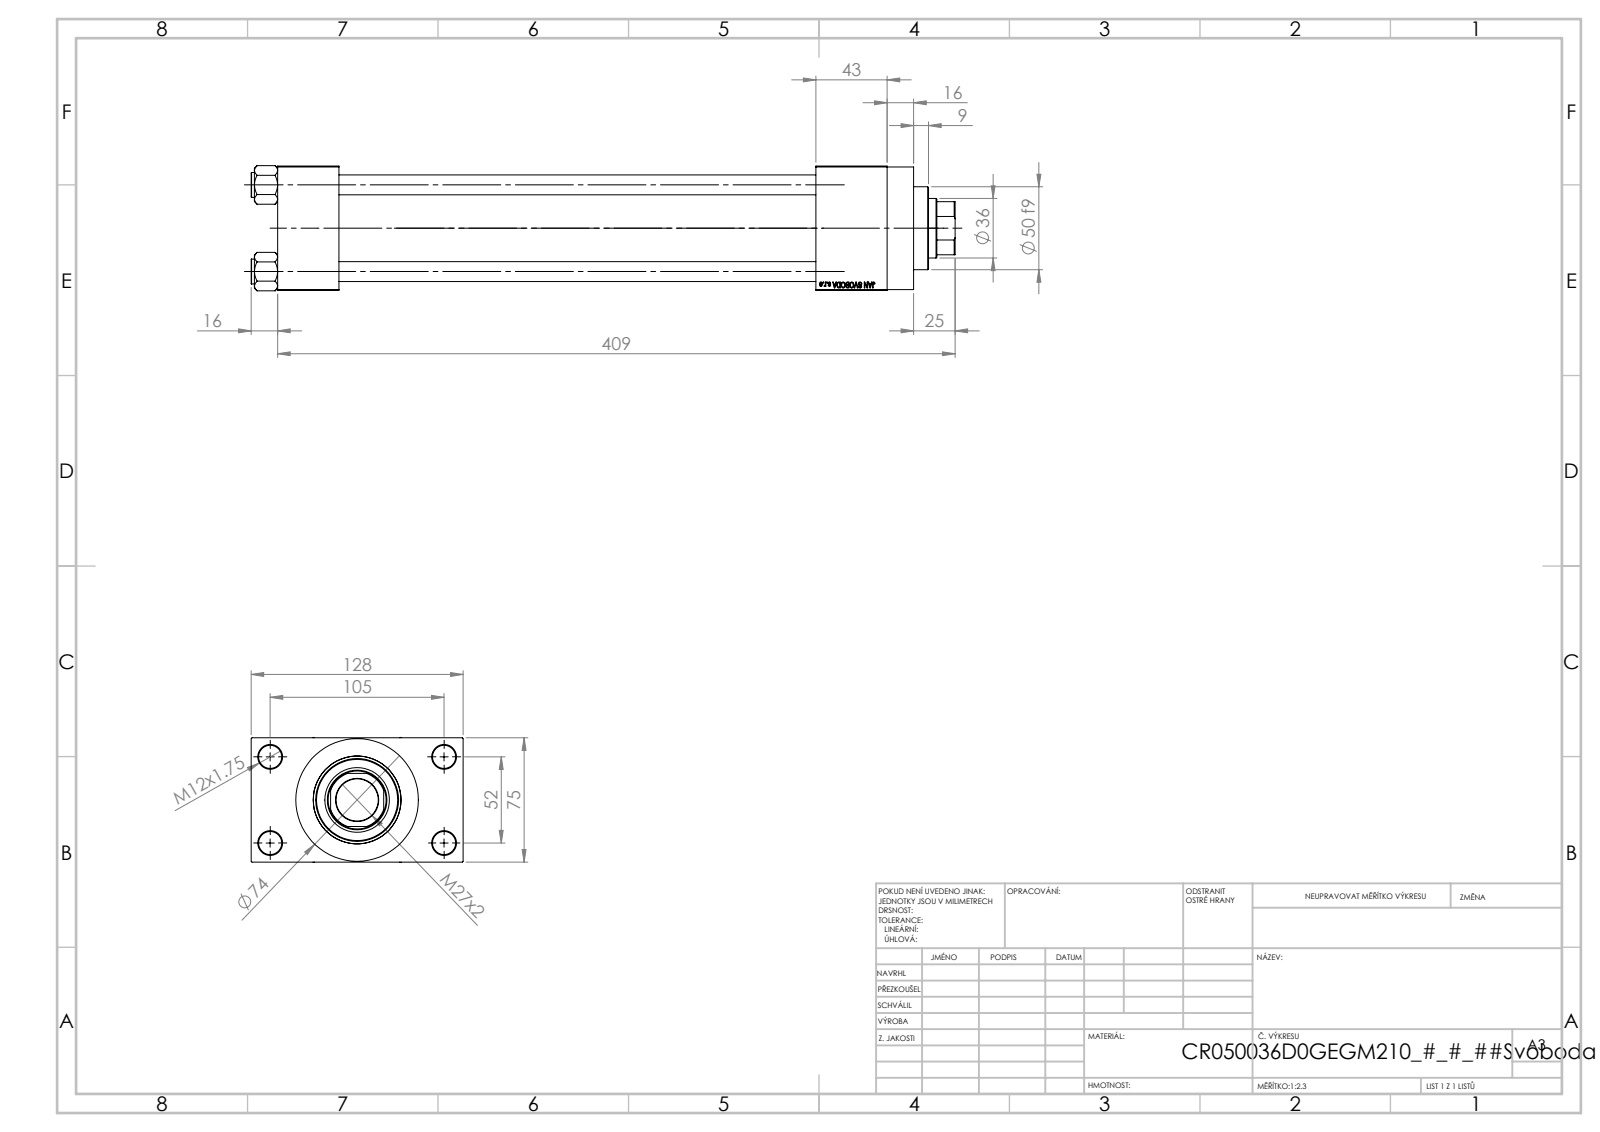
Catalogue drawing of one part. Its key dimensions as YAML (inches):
part_name: "V215CR_D_TYCINKA; NUT_M5_D; V215_VC_A; V215CR_VCP_D (+1 more)"
step_written_by: "SolidWorks 2019 (CONFIG_CONTROL_DESIGN)"
units: inches
bodies: {solids: 11, faces: 1104, planar: 497, cylindrical: 89, other: 518}
overall_size: [16.732, 5.039, 2.974]
volume: 78.05
surface_area: 482.2
round_holes:
  - {diameter: 0.472, count: 4}
  - {diameter: 0.551, count: 4}
  - {diameter: 0.276, count: 2}
  - {diameter: 0.825, count: 2}
  - {diameter: 1.181, count: 2}
  - {diameter: 1.004, count: 1}
  - {diameter: 1.417, count: 1}
  - {diameter: 1.535, count: 1}
  - {diameter: 1.614, count: 1}
  - {diameter: 2.087, count: 1}
round_bosses_or_shafts:
  - {diameter: 0.591, count: 4}
  - {diameter: 2.913, count: 1}
  - {diameter: 2.205, count: 1}
  - {diameter: 1.969, count: 1}
partial_cylinders:
  - {radius: 0.689, count: 1}
face_to_face_distances: [2.953, 11.339, 1.457, 12.795, 1.043, 3.996, 1.693, 14.488, 13.031, 0.63]
hole_center_spacings: [1.037, 1.456, 2.059, 2.3, 2.307, 3.096, 3.715, 2.047]
